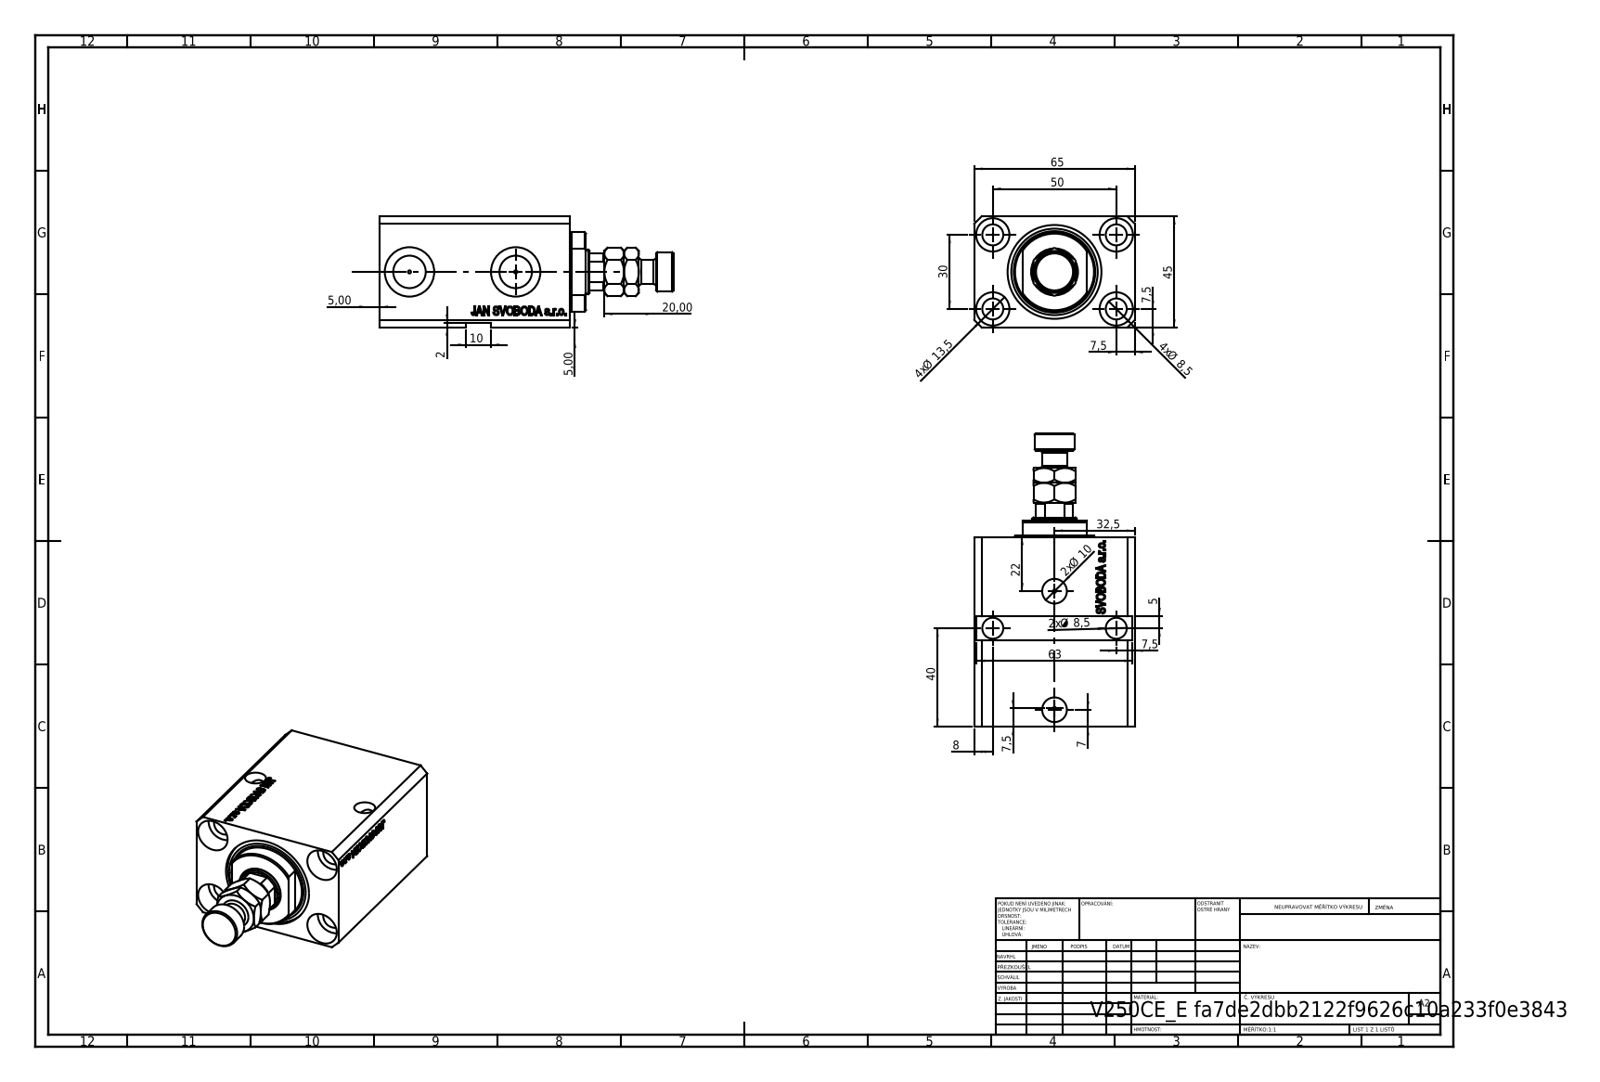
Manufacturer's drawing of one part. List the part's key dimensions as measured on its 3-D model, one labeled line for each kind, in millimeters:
Part name (STEP PRODUCT): V250CE_VC_E; V250CE_E_Body; MFA; V250CE_C_VCP
STEP written by: SolidWorks 2019 (CONFIG_CONTROL_DESIGN)
Units: millimetres
Bodies: 4 solids, 949 faces (451 planar, 88 cylindrical, 410 other)
Overall size (bounding box): 118.9 × 65 × 45
Volume: 197 130 mm³ · Surface area: 56 429 mm²
Round holes (diameter × count): ⌀8.5 ×7, ⌀1.25 ×4, ⌀13.5 ×4, ⌀10 ×2, ⌀13.16 ×2, ⌀20 ×2, ⌀18 ×1, ⌀25 ×1, ⌀38 ×1
Round bosses / shafts (diameter × count): ⌀16 ×1, ⌀10 ×1
Partial cylindrical surfaces — rounded edges, fillets, slot ends (radius × count): R8.5 ×1, R16 ×1
Main face-to-face distances: 45, 65, 51.9, 77, 25.1, 6.9, 70.1, 9, 68, 22.9
Hole centre spacings: 29.15, 50, 30, 40.98, 41.4, 58.31, 0.53, 43
